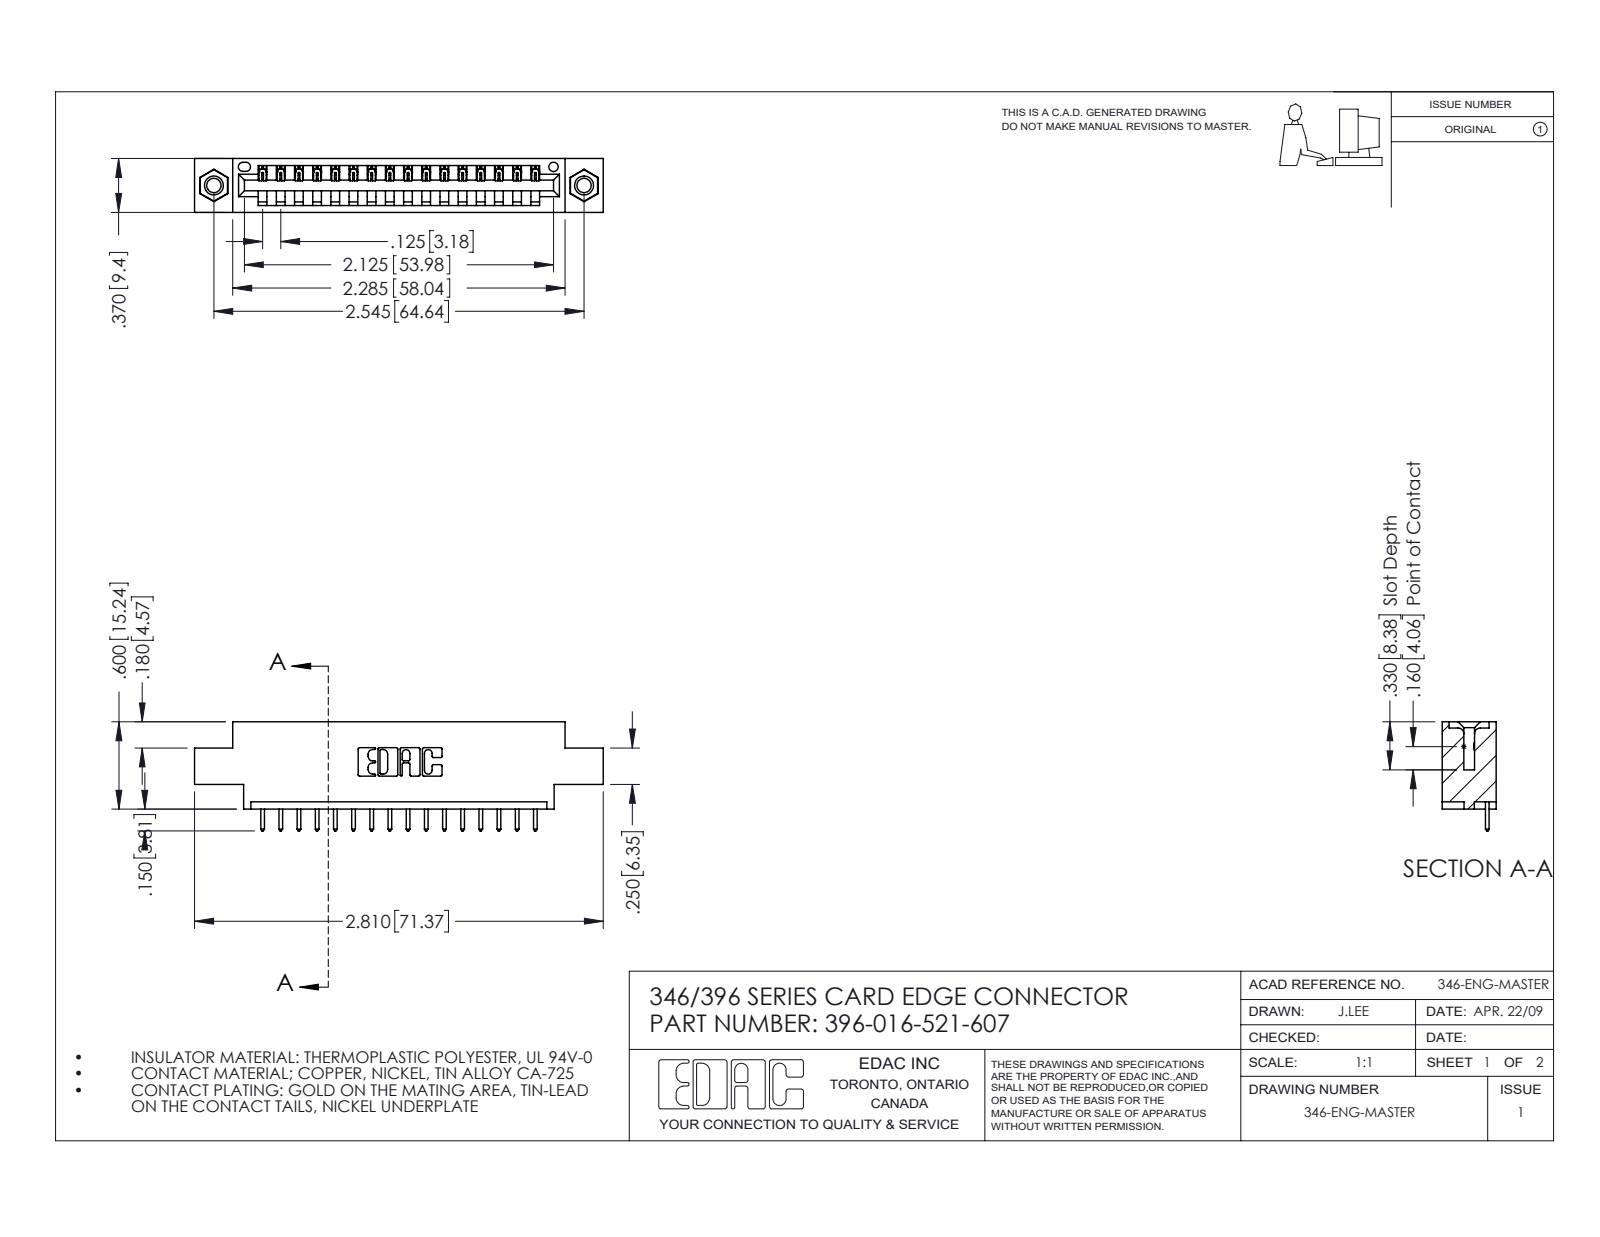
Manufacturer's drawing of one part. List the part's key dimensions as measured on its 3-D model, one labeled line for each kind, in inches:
Part name (STEP PRODUCT): 346 Part_0.170 Offset - 0.156 Dia-TI; 345-250-001_345-250-005-103; 396-016-521-607; 345-292-001_345-293-121
STEP written by: SolidWorks 2016 (CONFIG_CONTROL_DESIGN)
Units: inches
Bodies: 19 solids, 1114 faces (752 planar, 346 cylindrical, 16 other)
Overall size (bounding box): 2.81 × 0.75 × 0.37
Volume: 0.393 in³ · Surface area: 12.06 in²
Round holes (diameter × count): ⌀0.098 ×2, ⌀0.125 ×2, ⌀0.156 ×2, ⌀0.064 ×1
Round bosses / shafts (diameter × count): ⌀0.155 ×2
Partial cylindrical surfaces — rounded edges, fillets, slot ends (radius × count): R0.006 ×32, R0.01 ×32, R0.01 ×22, R0.007 ×6, R0.031 ×6, R0.026 ×3, R0.031 ×2, R0.04 ×2
Main face-to-face distances: 0.37, 0.048, 0.322, 0.25, 0.222, 0.148, 0.072, 0.298, 0.025, 0.1
Hole centre spacings: 0.246, 2.338, 2.545
